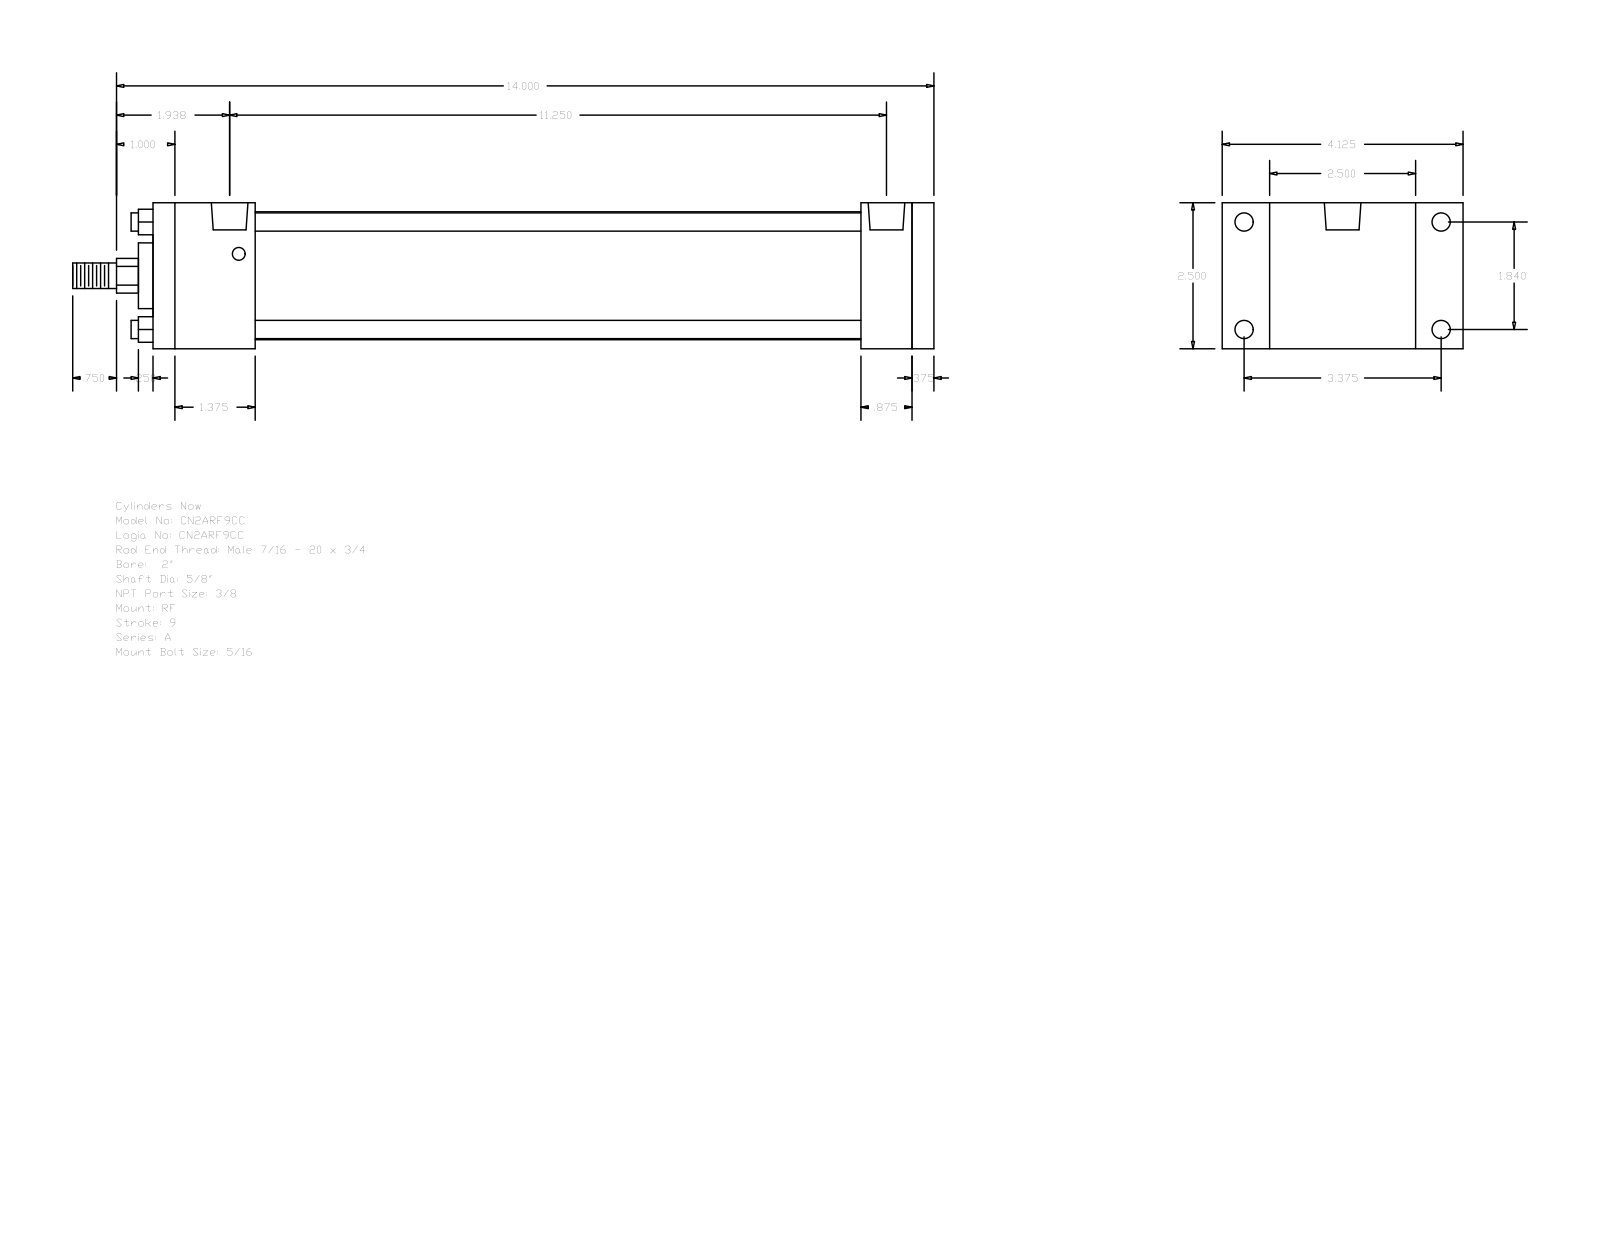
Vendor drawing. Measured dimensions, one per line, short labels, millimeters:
name: A_RF__0200_0.625
written by: GSSL Pune (CONFIG_CONTROL_DESIGN)
unit: mm
bodies: 0 solids, 92 faces (64 planar, 28 cylindrical, 0 other)
size: 374.65 × 104.78 × 63.5
holes: 4× ⌀5.56, 4× ⌀7.94, 2× ⌀15.93
bosses: 4× ⌀7.94, 1× ⌀55.63, 1× ⌀28.57, 1× ⌀15.88, 1× ⌀11.11
rounds: 1× R7.54
face distances: 63.5, 339.72, 9.53, 330.19, 44.45, 285.74, 295.27, 307.97, 263.52, 22.22
hole spacings: 46.74, 85.72, 97.63, 277.8, 3.97, 3.98, 281.77, 281.78
